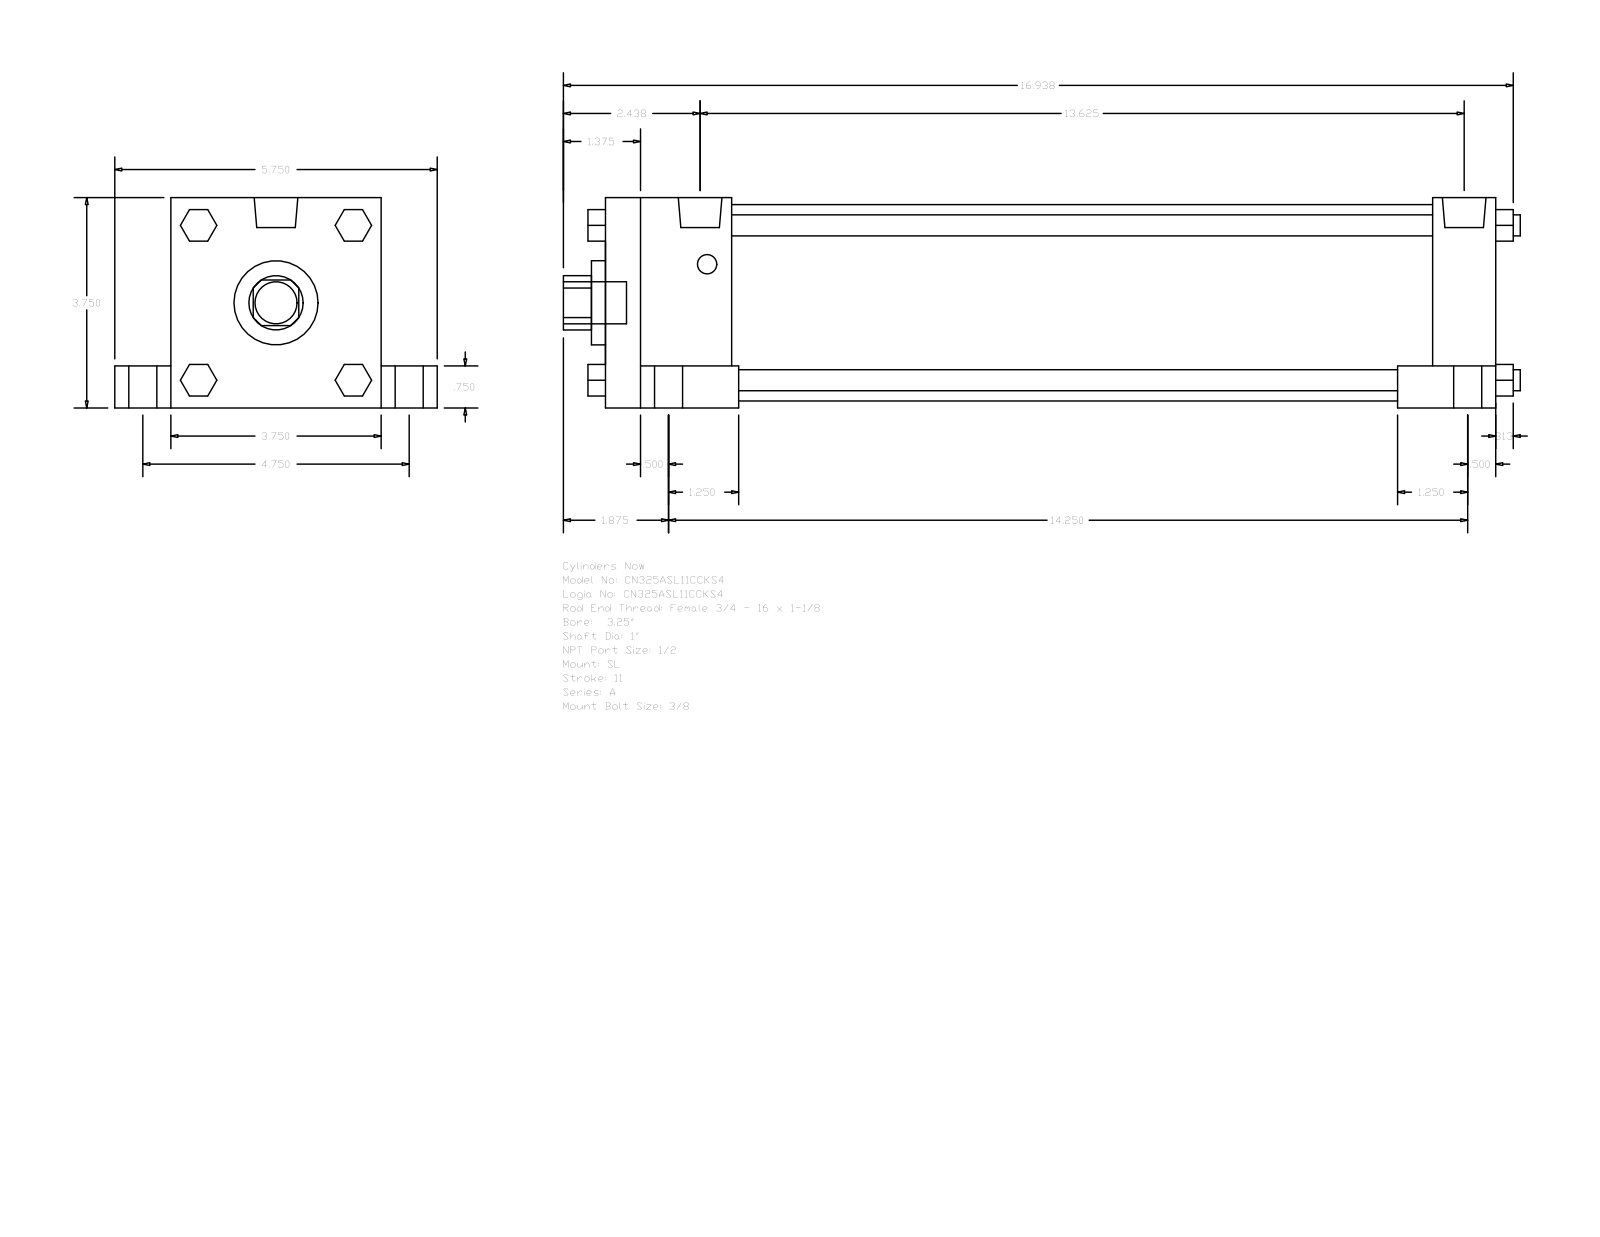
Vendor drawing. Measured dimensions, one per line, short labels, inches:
name: A_SL__0325_1
written by: GSSL Pune (CONFIG_CONTROL_DESIGN)
unit: in
bodies: 0 solids, 150 faces (114 planar, 36 cylindrical, 0 other)
size: 17.063 × 5.75 × 3.75
holes: 1× ⌀1, 1× ⌀1.5, 1× ⌀3.5
bosses: 5× ⌀0.75, 4× ⌀0.5, 4× ⌀0.375, 4× ⌀0.344, 2× ⌀0.778
rounds: 1× R0.484
face distances: 3.75, 15.875, 0.75, 1, 4.75, 3, 1.125, 2.25, 14.75, 12.5
